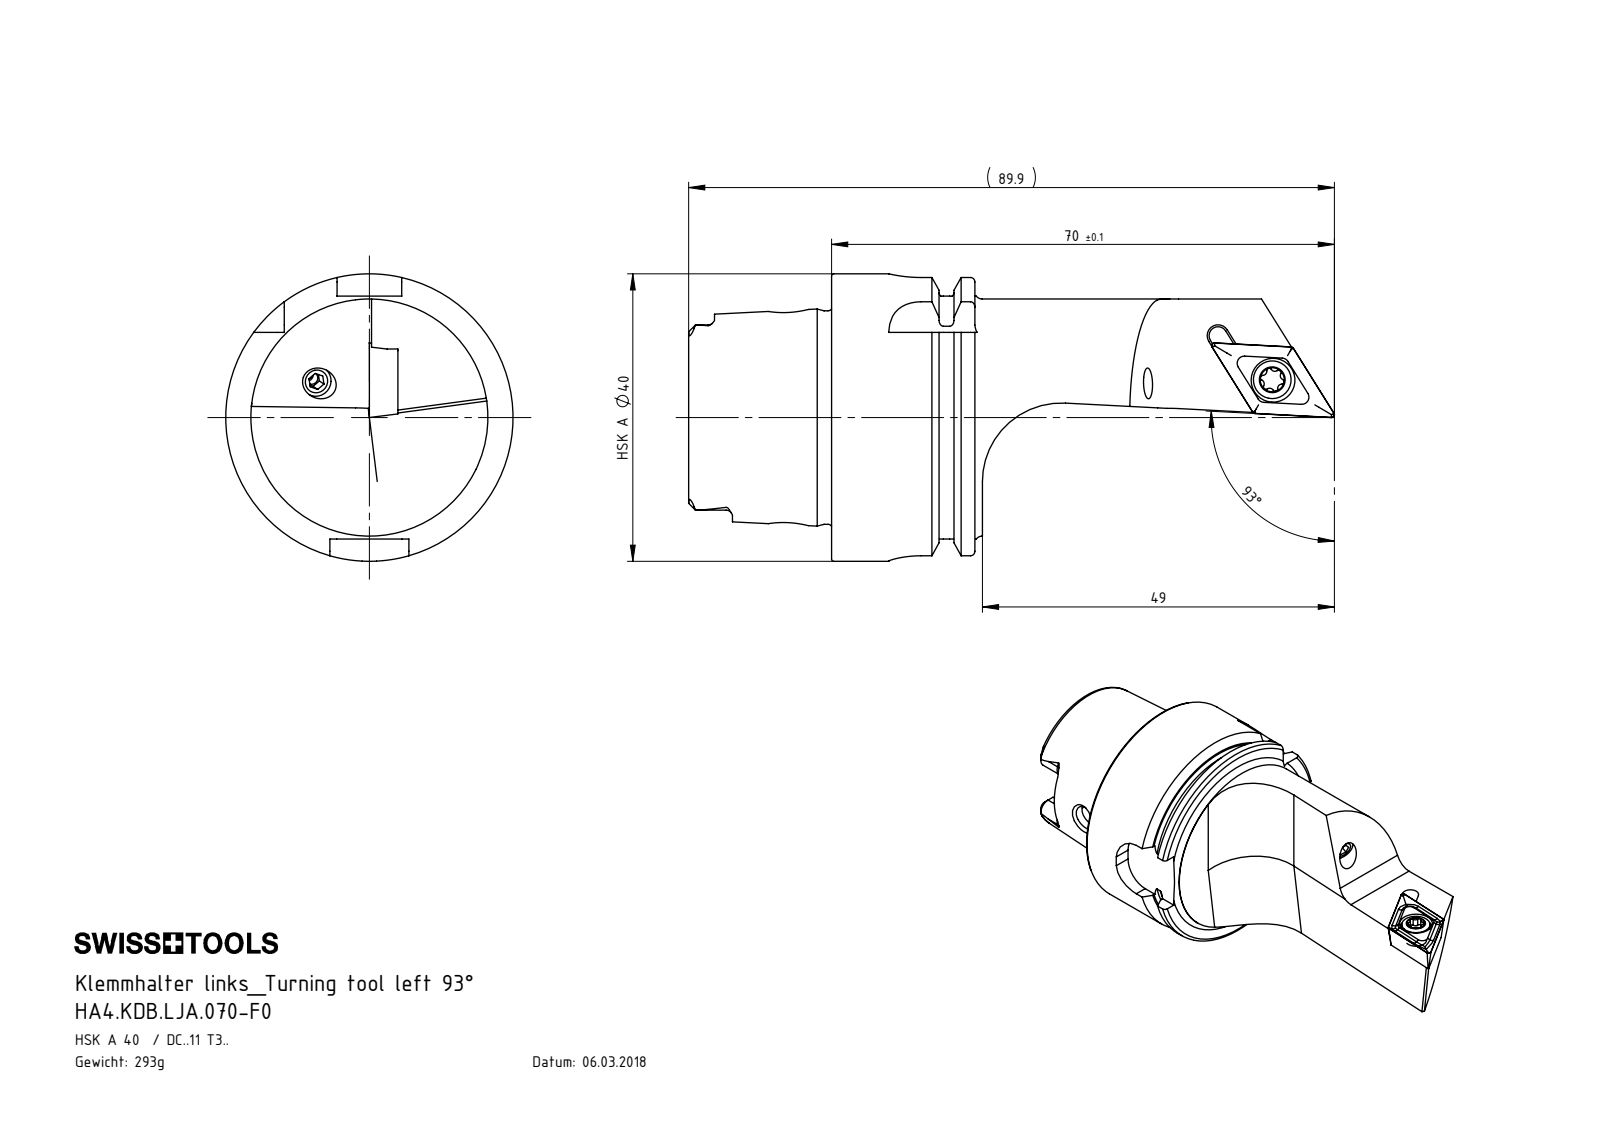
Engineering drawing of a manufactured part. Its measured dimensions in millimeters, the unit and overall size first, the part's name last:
Units: millimetres
Overall size (bounding box): 89.91 × 40 × 40
Round holes (diameter × count): ⌀3.3 ×4, ⌀3 ×2, ⌀4 ×2, ⌀1.7 ×1, ⌀4.2 ×1, ⌀4.4 ×1, ⌀4.6 ×1, ⌀6.1 ×1, ⌀10 ×1, ⌀11 ×1, ⌀12.5 ×1, ⌀21 ×1
Round bosses / shafts (diameter × count): ⌀4 ×4, ⌀40 ×1, ⌀34.75 ×1, ⌀33 ×1, ⌀29.71 ×1, ⌀5.25 ×1
Partial cylindrical surfaces — rounded edges, fillets, slot ends (radius × count): R0.34 ×6, R0.59 ×6, R0.9 ×6, R1.88 ×4, R4.5 ×4, R1.25 ×1, R3 ×1, R11 ×1
Main face-to-face distances: 7.95, 19.95, 12, 21, 13.05, 1.05, 3.67, 19.9, 27.85, 39.85
Hole centre spacings: 54.6, 54.71
Volume: 37 019 mm³ · Surface area: 14 141 mm²
Bodies: 8 solids, 269 faces (90 planar, 67 cylindrical, 112 other)
Part name (STEP PRODUCT): HA4-KDB.LJA.070-F0_A_Fertigbearbeitung; KVT_MB_600_040; WCB-ER2.001.009_A; DCMT11T304 (+2 more)
STEP written by: SolidWorks 2017 (AUTOMOTIVE_DESIGN)
